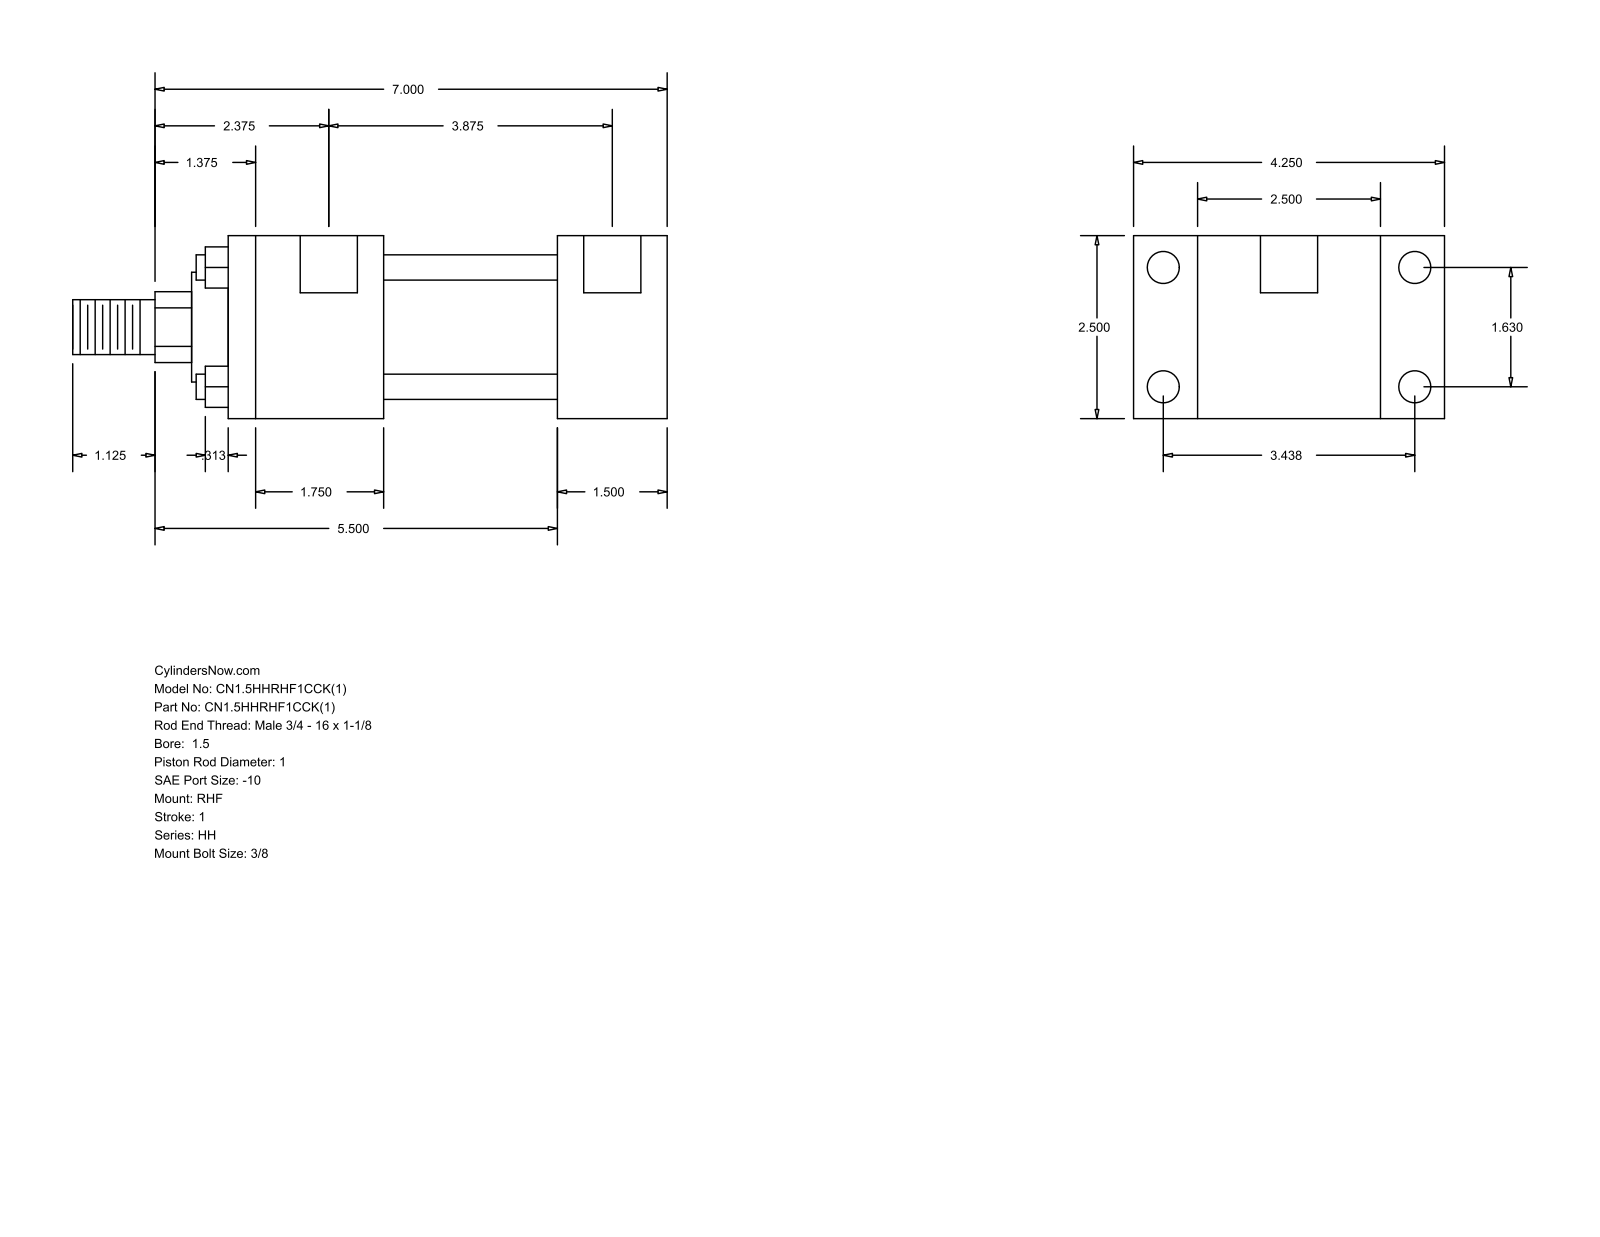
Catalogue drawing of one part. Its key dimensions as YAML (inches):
part_name: "HH_RHF__0150_1"
step_written_by: "GSSL Pune (CONFIG_CONTROL_DESIGN)"
units: inches
bodies: {solids: 0, faces: 88, planar: 60, cylindrical: 28, other: 0}
overall_size: [8.125, 4.25, 2.5]
round_holes:
  - {diameter: 0.219, count: 4}
  - {diameter: 0.438, count: 4}
  - {diameter: 0.781, count: 2}
round_bosses_or_shafts:
  - {diameter: 0.345, count: 4}
  - {diameter: 1.75, count: 1}
  - {diameter: 1.5, count: 1}
  - {diameter: 1, count: 1}
  - {diameter: 0.75, count: 1}
partial_cylinders:
  - {radius: 0.484, count: 1}
face_to_face_distances: [2.5, 0.875, 3.375, 1.5, 4.25, 2.375, 3.875, 2.125, 4.5, 6]
hole_center_spacings: [0.063, 1.63, 3.438, 3.805, 3.937, 4, 3.875]
